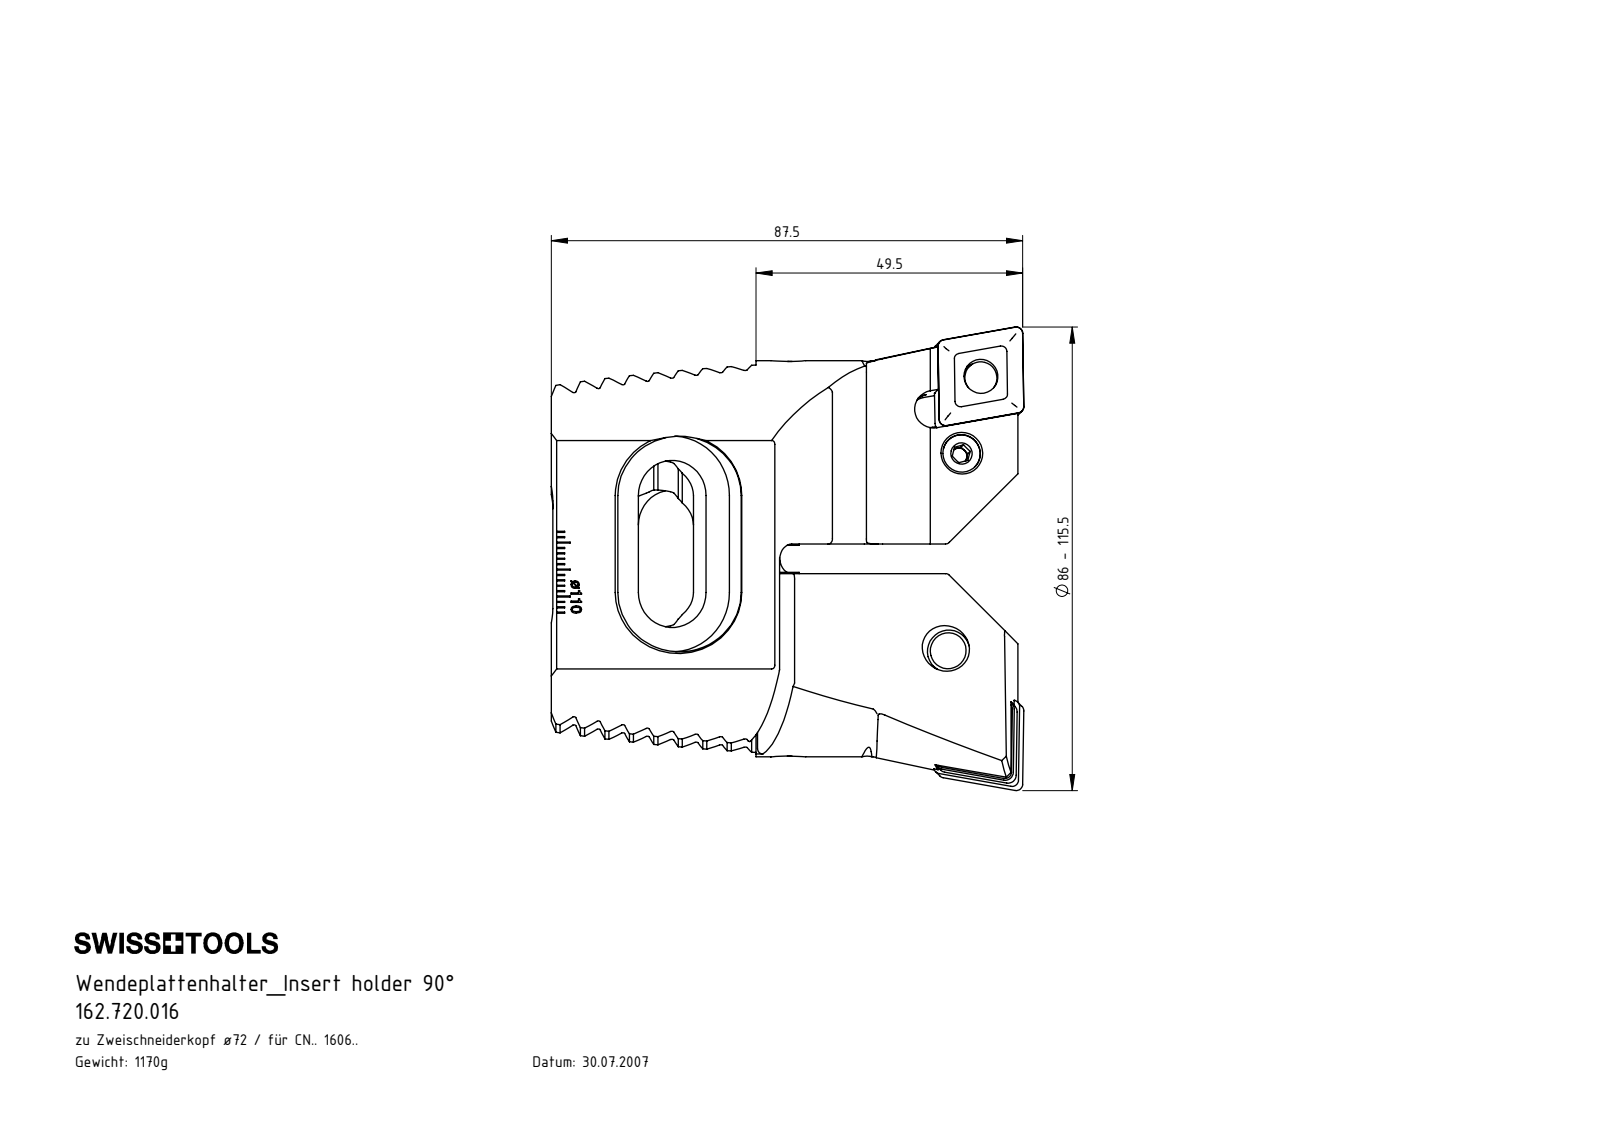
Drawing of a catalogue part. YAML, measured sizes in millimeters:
part_name: "Z72-ER3.001.030; CNMG160612; WCE; WCE-ER2.101.004_A (+5 more)"
step_written_by: "SolidWorks 2017 (CONFIG_CONTROL_DESIGN)"
units: millimeters
bodies: {solids: 14, faces: 912, planar: 486, cylindrical: 178, other: 248}
overall_size: [87.72, 86, 58.2]
volume: 148078
surface_area: 43960
round_holes:
  - {diameter: 2, count: 2}
  - {diameter: 6.35, count: 2}
  - {diameter: 7, count: 2}
  - {diameter: 8.05, count: 2}
  - {diameter: 8.4, count: 2}
  - {diameter: 5, count: 1}
round_bosses_or_shafts:
  - {diameter: 6, count: 3}
  - {diameter: 8, count: 2}
  - {diameter: 7.9, count: 2}
  - {diameter: 6.4, count: 2}
  - {diameter: 3.55, count: 2}
  - {diameter: 4, count: 1}
partial_cylinders:
  - {radius: 0.34, count: 16}
  - {radius: 1, count: 16}
  - {radius: 1.2, count: 8}
  - {radius: 1.5, count: 8}
  - {radius: 3, count: 6}
  - {radius: 3.5, count: 6}
  - {radius: 0.3, count: 4}
  - {radius: 6.5, count: 4}
face_to_face_distances: [4.07, 8.14, 20.36, 12.21, 16.29, 20.34, 24.43, 1.61, 58.2, 16.27]
hole_center_spacings: [14.76, 15, 20, 38.64]
